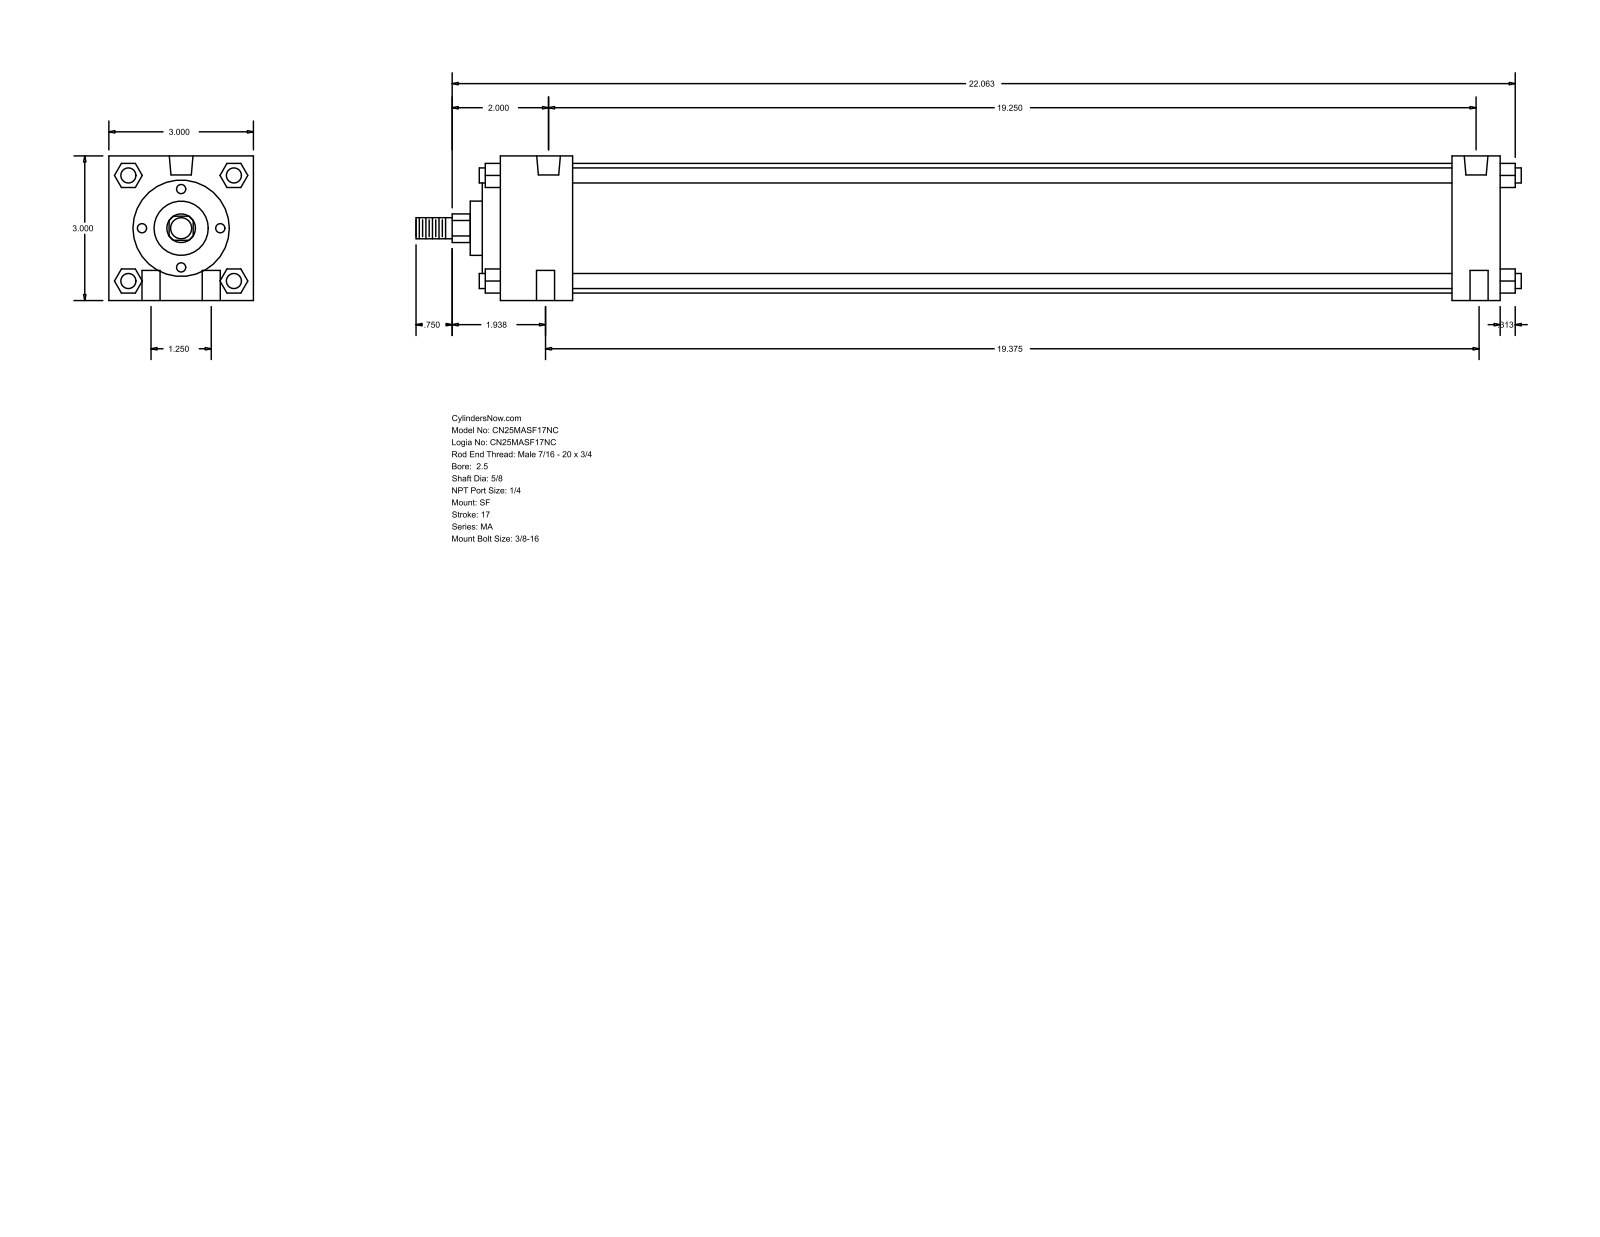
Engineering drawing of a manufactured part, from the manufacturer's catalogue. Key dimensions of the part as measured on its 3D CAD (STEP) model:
Part name (STEP PRODUCT): MA_SF__0250_0.625
STEP written by: GSSL Pune (CONFIG_CONTROL_DESIGN)
Units: millimetres
Bodies: 0 solids, 126 faces (95 planar, 31 cylindrical, 0 other)
Overall size (bounding box): 582.61 × 76.2 × 76.2
Round holes (diameter × count): ⌀9.53 ×4, ⌀7.94 ×2, ⌀12.49 ×2
Round bosses / shafts (diameter × count): ⌀7.94 ×4, ⌀68.33 ×1, ⌀50.8 ×1, ⌀28.57 ×1, ⌀15.88 ×1, ⌀11.11 ×1
Partial cylindrical surfaces — rounded edges, fillets, slot ends (radius × count): R7.54 ×1
Main face-to-face distances: 76.2, 527.05, 25.4, 501.65, 38.1, 463.55, 488.95, 12.7, 9.52, 47.62
Hole centre spacings: 15.96, 490.8, 31.76, 488.95, 492.13, 493.15
